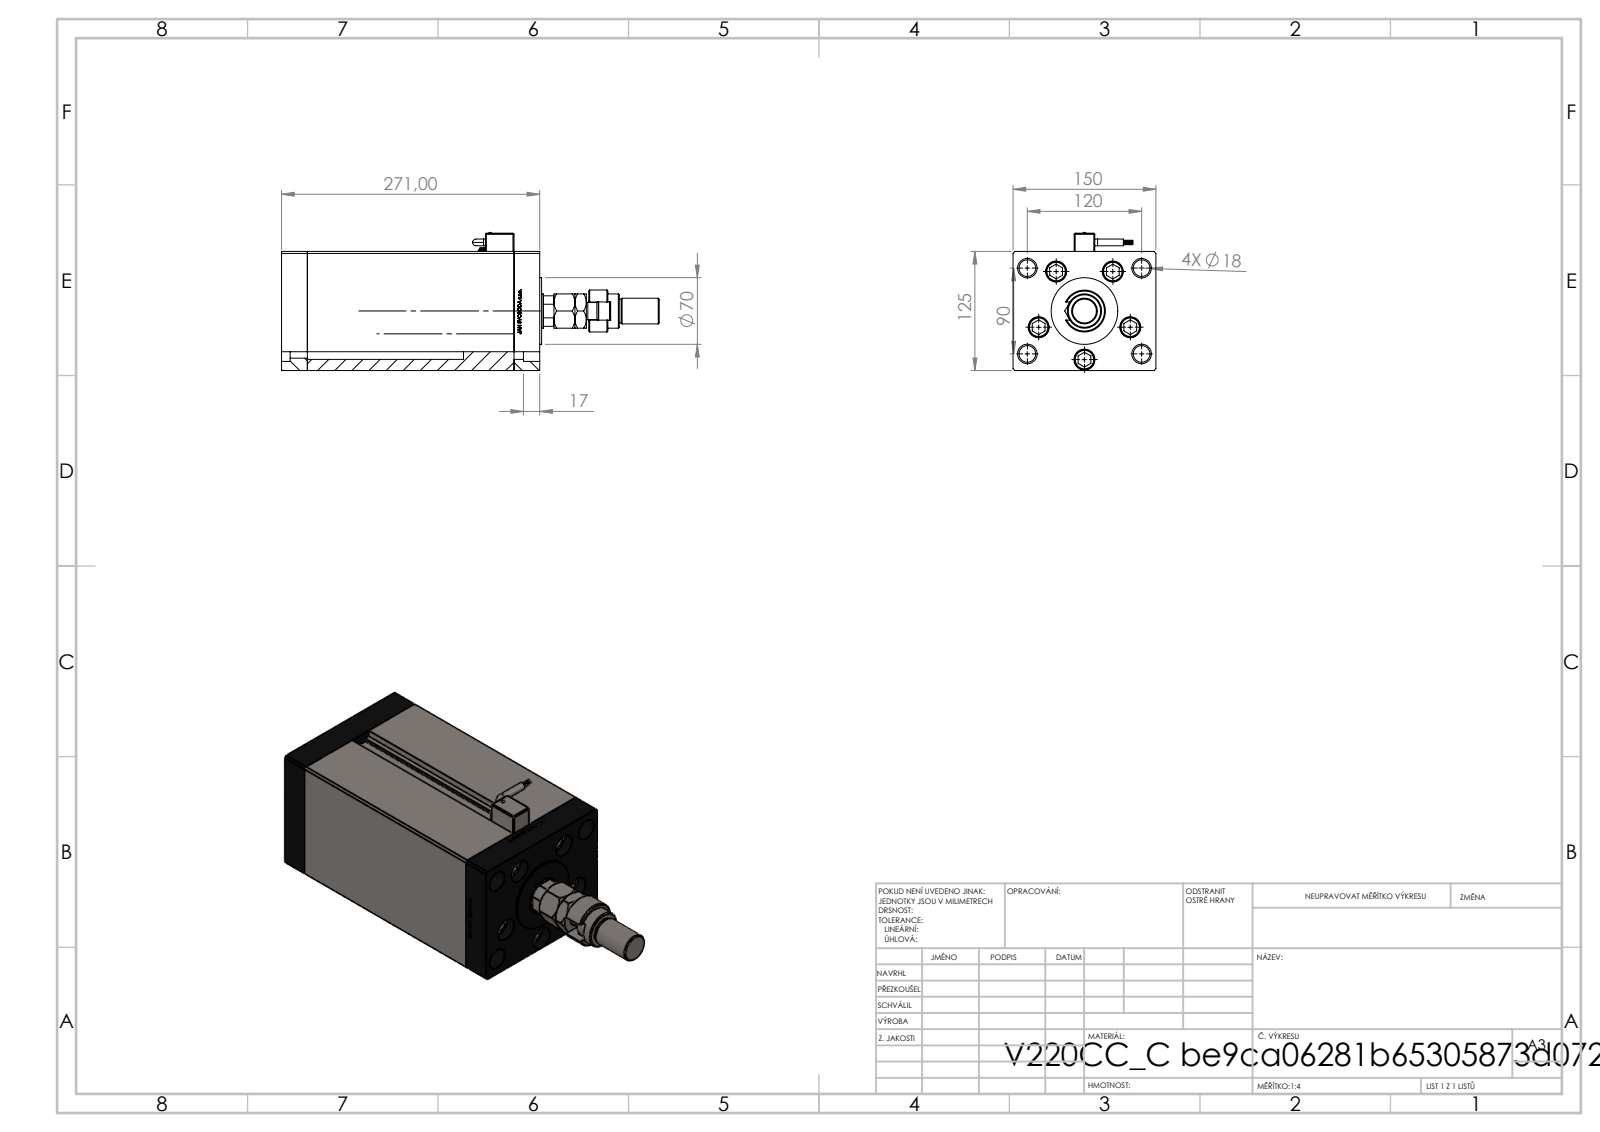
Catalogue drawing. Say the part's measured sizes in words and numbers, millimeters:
The part is named "V220C_C MIDDLE; FEMALE_PART_FOR_DFA; V220C_VC_C; Magnetic_Switch_MSU4 (+4 more)". Its 3-D file was written by "SolidWorks 2019 (CONFIG_CONTROL_DESIGN)". It is 16 solids with 1350 faces: 609 planar, 217 cylindrical and 524 other. Overall it measures 396.5 by 150 by 145.1 millimeters. Its volume is 4 245 000 cubic millimeters and its surface area 476 648 square millimeters. Round holes: 9 of diameter 17.5, 5 of diameter 22, 4 of diameter 16, 4 of diameter 20.5, 1 of diameter 3.6, 1 of diameter 5, 1 of diameter 7, 1 of diameter 21, 1 of diameter 25.5. Round bosses or shafts: 5 of diameter 8, 4 of diameter 21, 4 of diameter 0.85, 2 of diameter 7, 1 of diameter 80, 1 of diameter 70, 1 of diameter 44, 1 of diameter 36. Partial cylindrical surfaces (rounded edges, fillets, slot ends): 14 of radius 1, 2 of radius 0.93, 2 of radius 4, 1 of radius 9.5, 1 of radius 15, 1 of radius 17.5. The main face-to-face distances are 150, 125, 27, 244, 217, 33.5, 6.5, 271, 237.5, 210.5. The hole center spacings are 51, 75, 30.43, 30.48, 58.89, 60.3, 61.25, 63.14.
